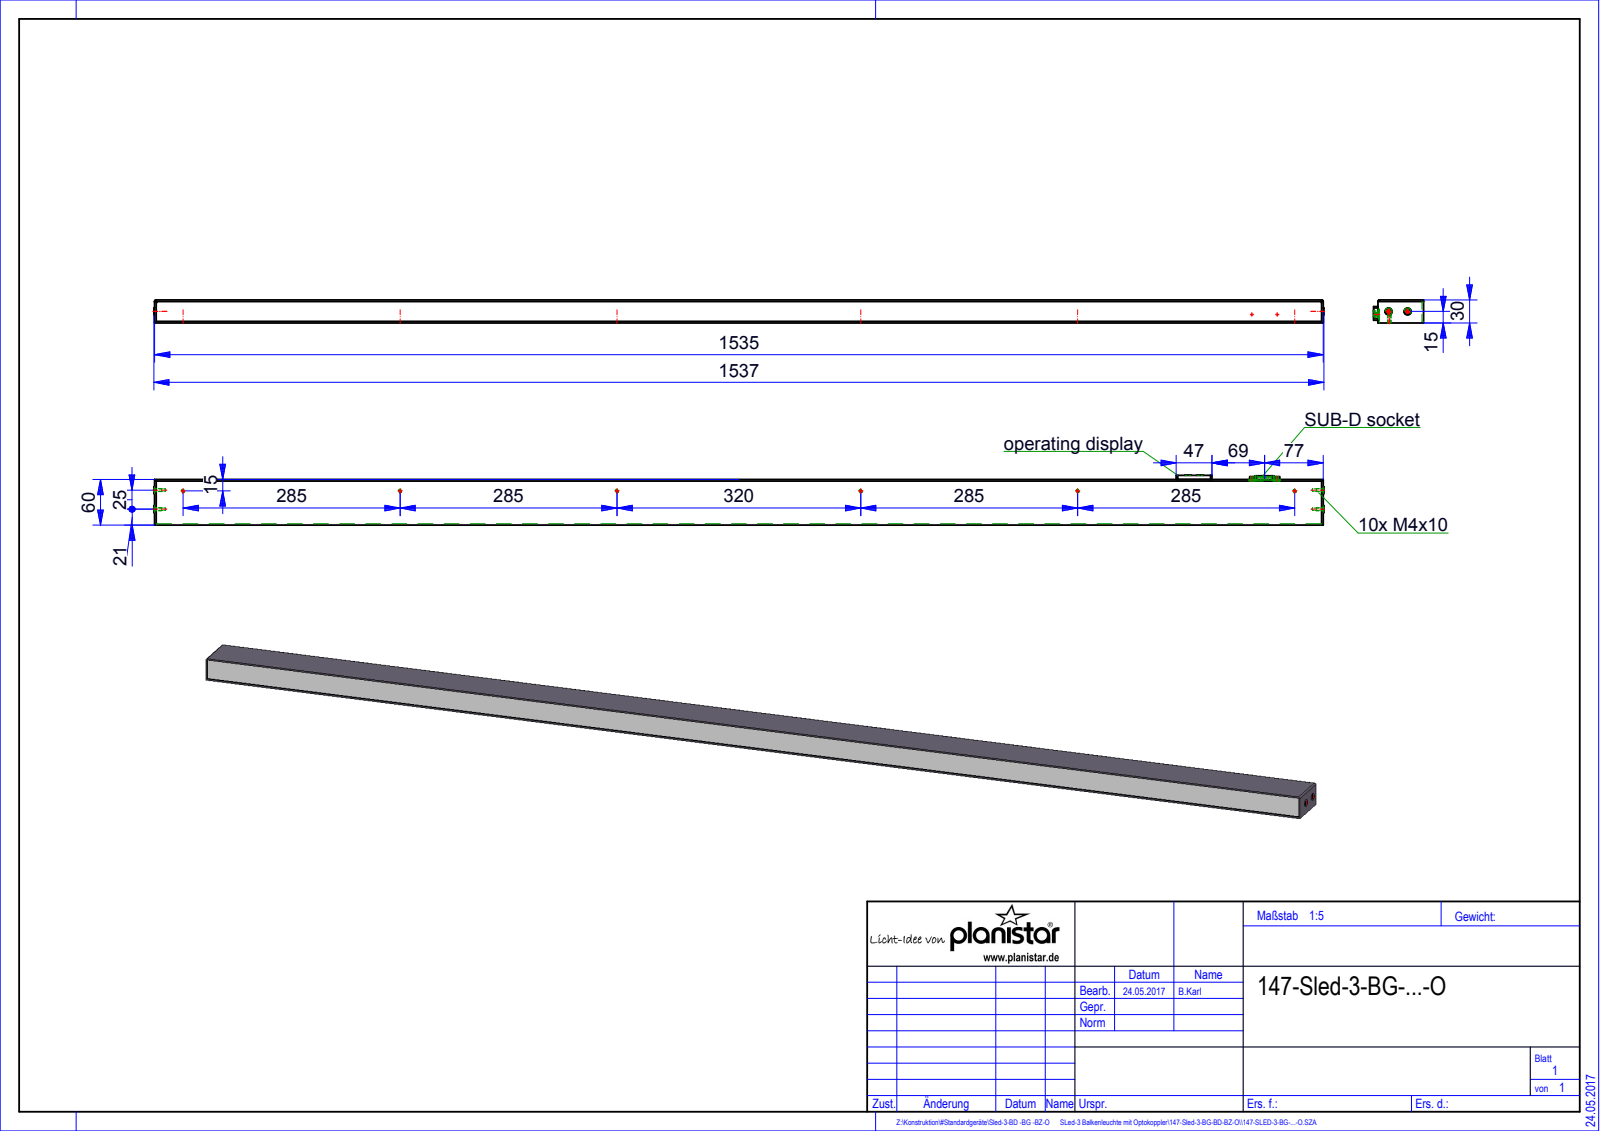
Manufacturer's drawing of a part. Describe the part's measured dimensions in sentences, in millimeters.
The part is named "Root; Baugruppe_Balkenleuchte; QUADER_3; Baugruppe_Baugruppe (+6 more)". Its 3-D file was written by "HiCAD 2015 2002.1 Build 408 (AUTOMOTIVE_DESIGN)". It is 12 solids with 176 faces: 85 planar, 72 cylindrical and 19 other. Overall it measures 1537 by 65.6 by 30 millimeters. Its volume is 2 685 000 cubic millimeters and its surface area 291 423 square millimeters. Round holes: 8 of diameter 3.3, 8 of diameter 4, 2 of diameter 2.5, 2 of diameter 3. Round bosses or shafts: 5 of diameter 1, 2 of diameter 9, 2 of diameter 8, 2 of diameter 3.6. Partial cylindrical surfaces (rounded edges, fillets, slot ends): 12 of radius 0.2, 7 of radius 2, 6 of radius 2.5, 4 of radius 1.5, 4 of radius 2.1, 2 of radius 1. The main face-to-face distances are 30, 58, 2, 60, 28, 26, 1535, 1, 56, 6.5. The hole center spacings are 285, 890, 570, 605, 1175, 25, 33.32, 320.
